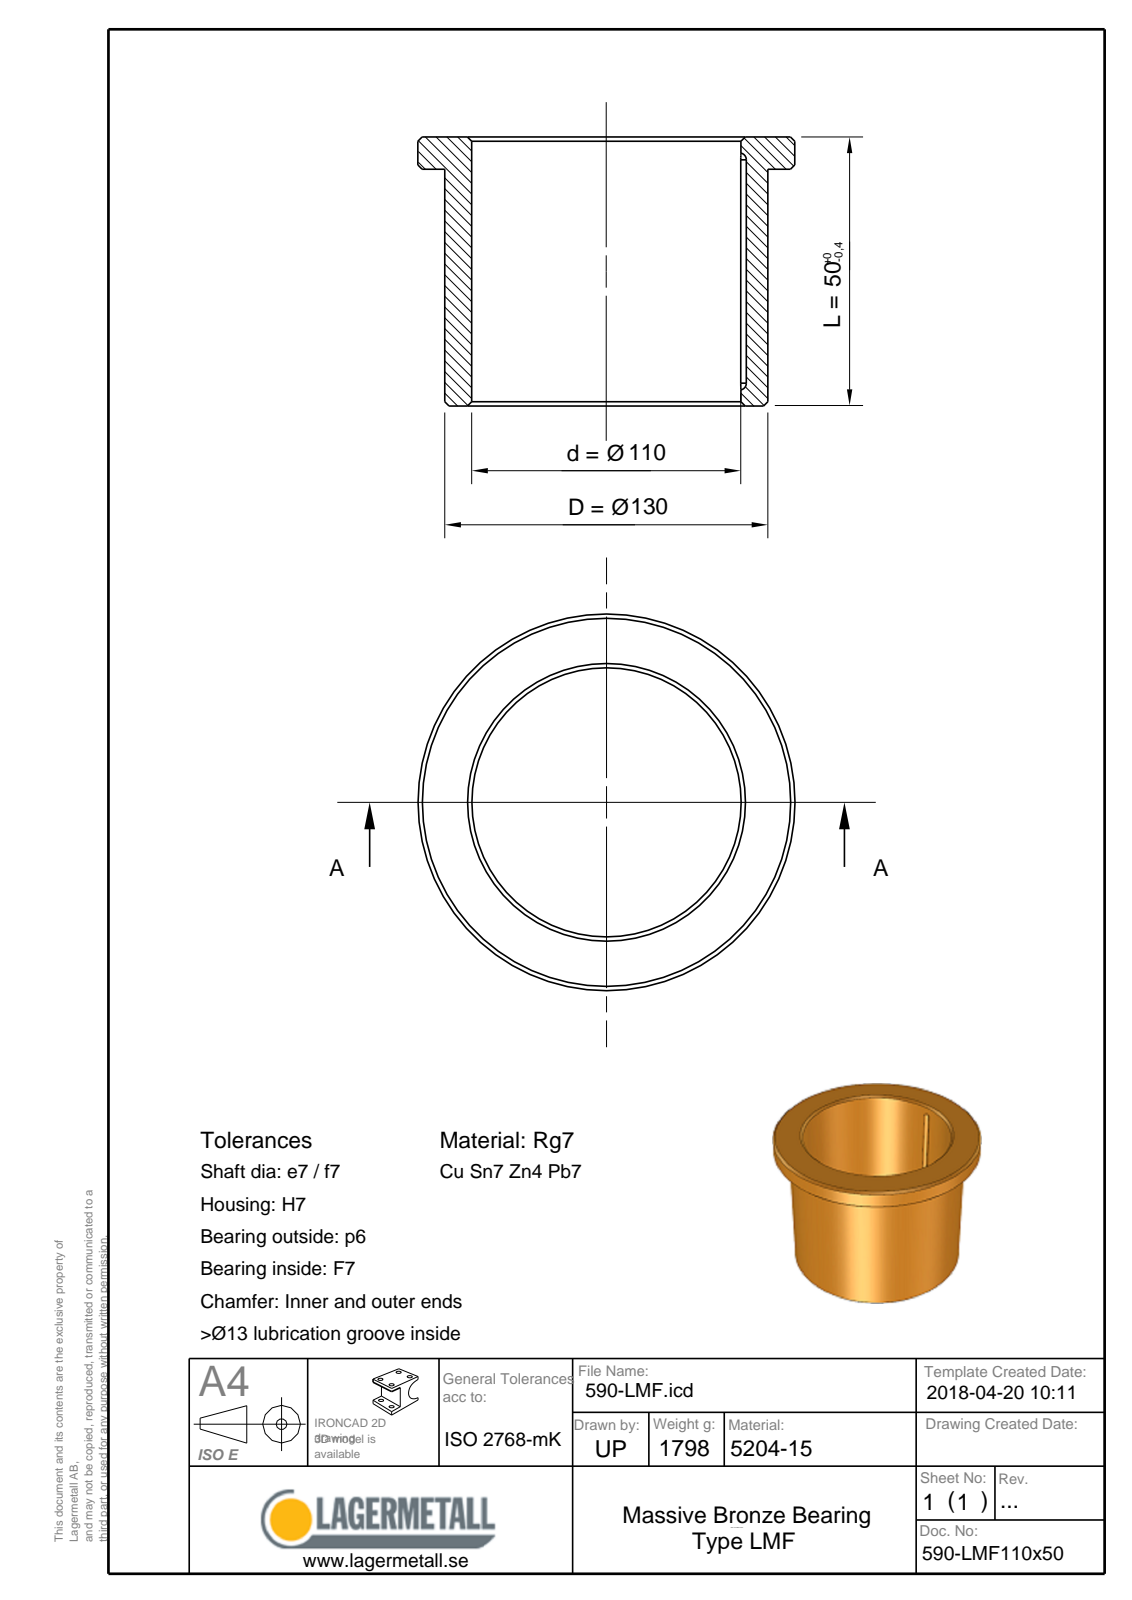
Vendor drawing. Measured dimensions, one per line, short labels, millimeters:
name: 590-LMF110x50
written by: Spatial InterOp 3D (CONFIG_CONTROL_DESIGN)
unit: mm
bodies: 1 solid, 16 faces (4 planar, 5 cylindrical, 7 other)
size: 140 × 140 × 50
volume: 204 308 mm³; area: 48 639 mm²
holes: 1× ⌀110
bosses: 1× ⌀140, 1× ⌀130
rounds: 2× R1.75
face distances: 50, 42, 8
